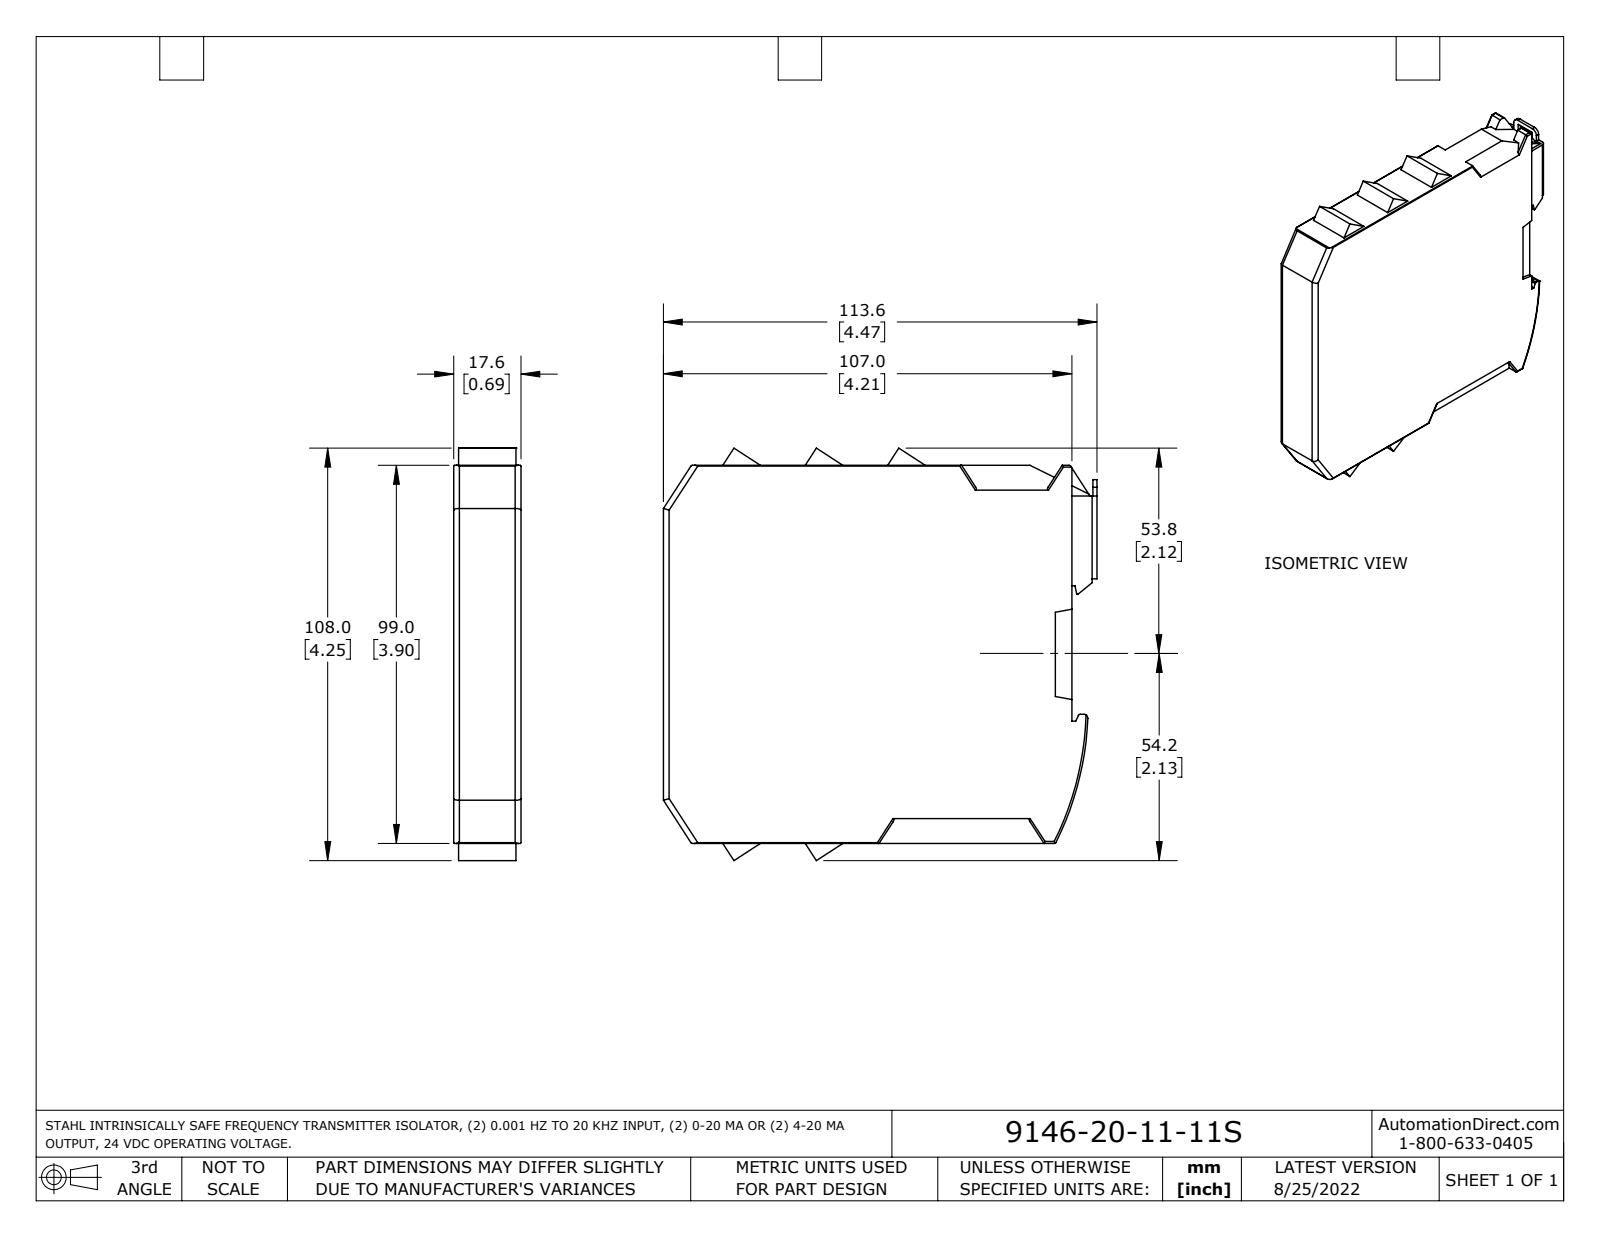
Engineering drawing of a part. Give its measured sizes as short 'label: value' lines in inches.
name: 9146-20-11-11S
written by: SolidWorks 2021 (AUTOMOTIVE_DESIGN)
unit: in
bodies: 2 solids, 181 faces (127 planar, 52 cylindrical, 2 other)
size: 4.472 × 4.252 × 0.693
volume: 11.44 in³; area: 46.75 in²
rounds: 17× R0.02, 6× R0.059, 4× R0.008, 4× R0.028, 2× R0.051, 2× R0.079, 1× R0.039, 1× R3.15
face distances: 0.693, 3.898, 4.213, 0.041, 0.652, 0.217, 4.429, 0.043, 0.26, 4.472
